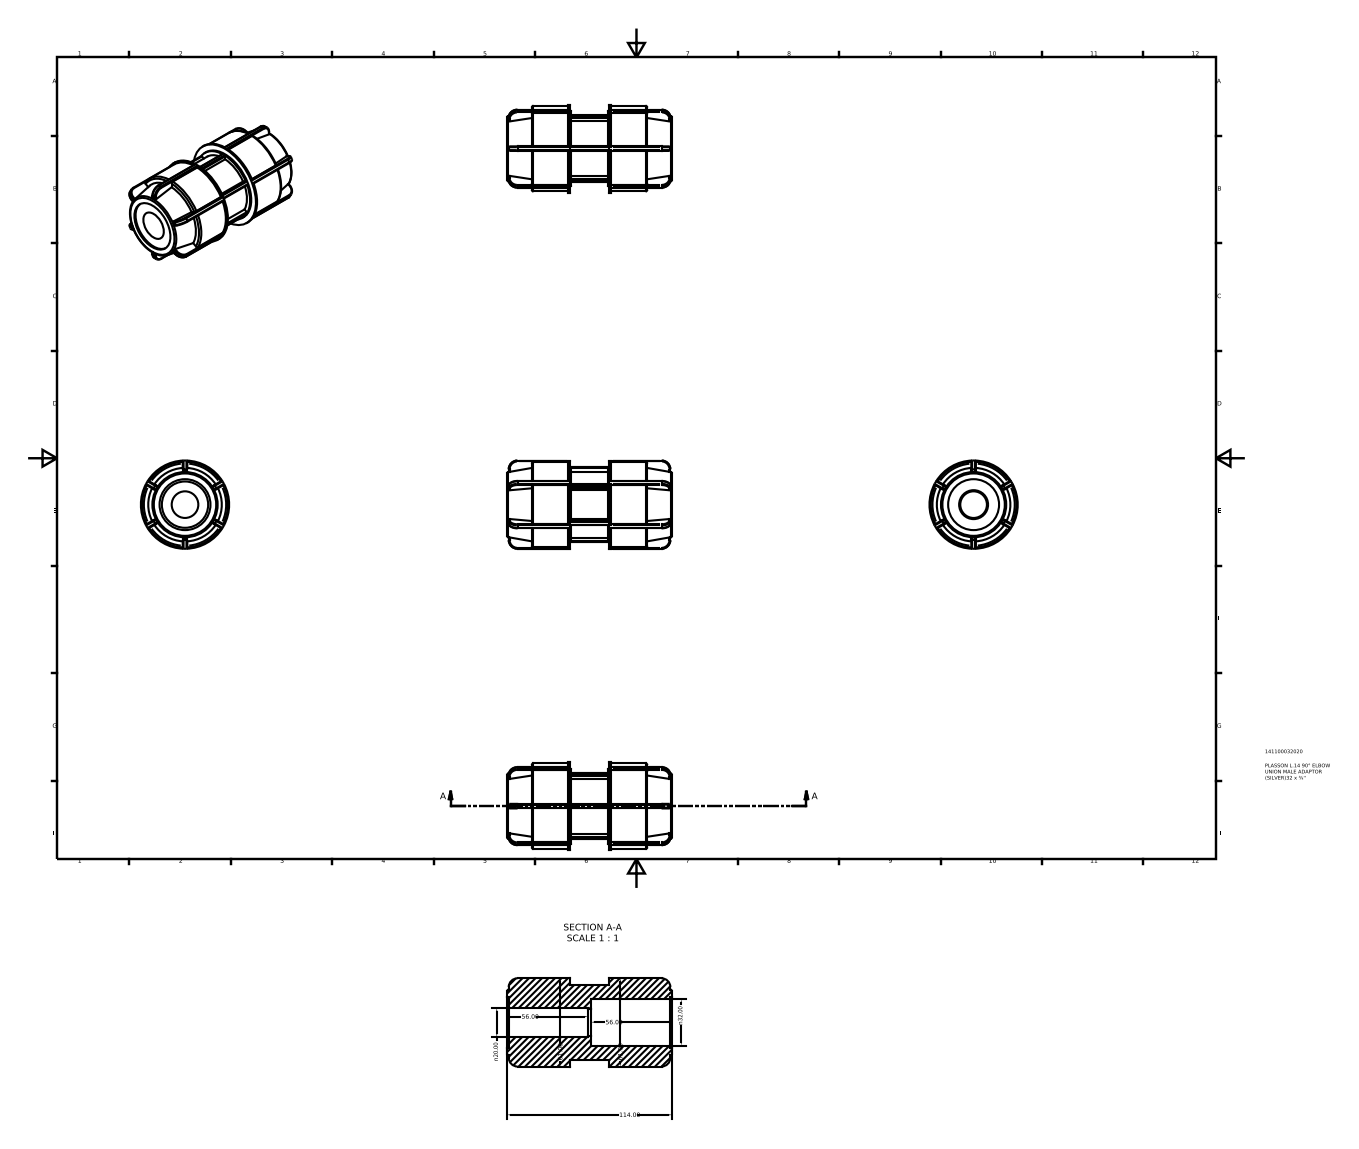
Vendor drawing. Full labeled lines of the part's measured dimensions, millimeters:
Part name (STEP PRODUCT): 141100032020
STEP written by: Autodesk Inventor 2015 (AUTOMOTIVE_DESIGN)
Units: millimetres
Bodies: 1 solid, 230 faces (92 planar, 86 cylindrical, 52 other)
Overall size (bounding box): 114 × 61 × 61
Volume: 193 741 mm³ · Surface area: 38 334 mm²
Round holes (diameter × count): ⌀18.4 ×1, ⌀20 ×1, ⌀32 ×1, ⌀35.2 ×1
Round bosses / shafts (diameter × count): ⌀61 ×1, ⌀59.17 ×1, ⌀51.85 ×1, ⌀45.75 ×1
Partial cylindrical surfaces — rounded edges, fillets, slot ends (radius × count): R0.61 ×44
Main face-to-face distances: 27.36, 1.14, 26.22, 69.54, 43.32, 70.68, 42.18, 3.2, 17.1, 96.9
